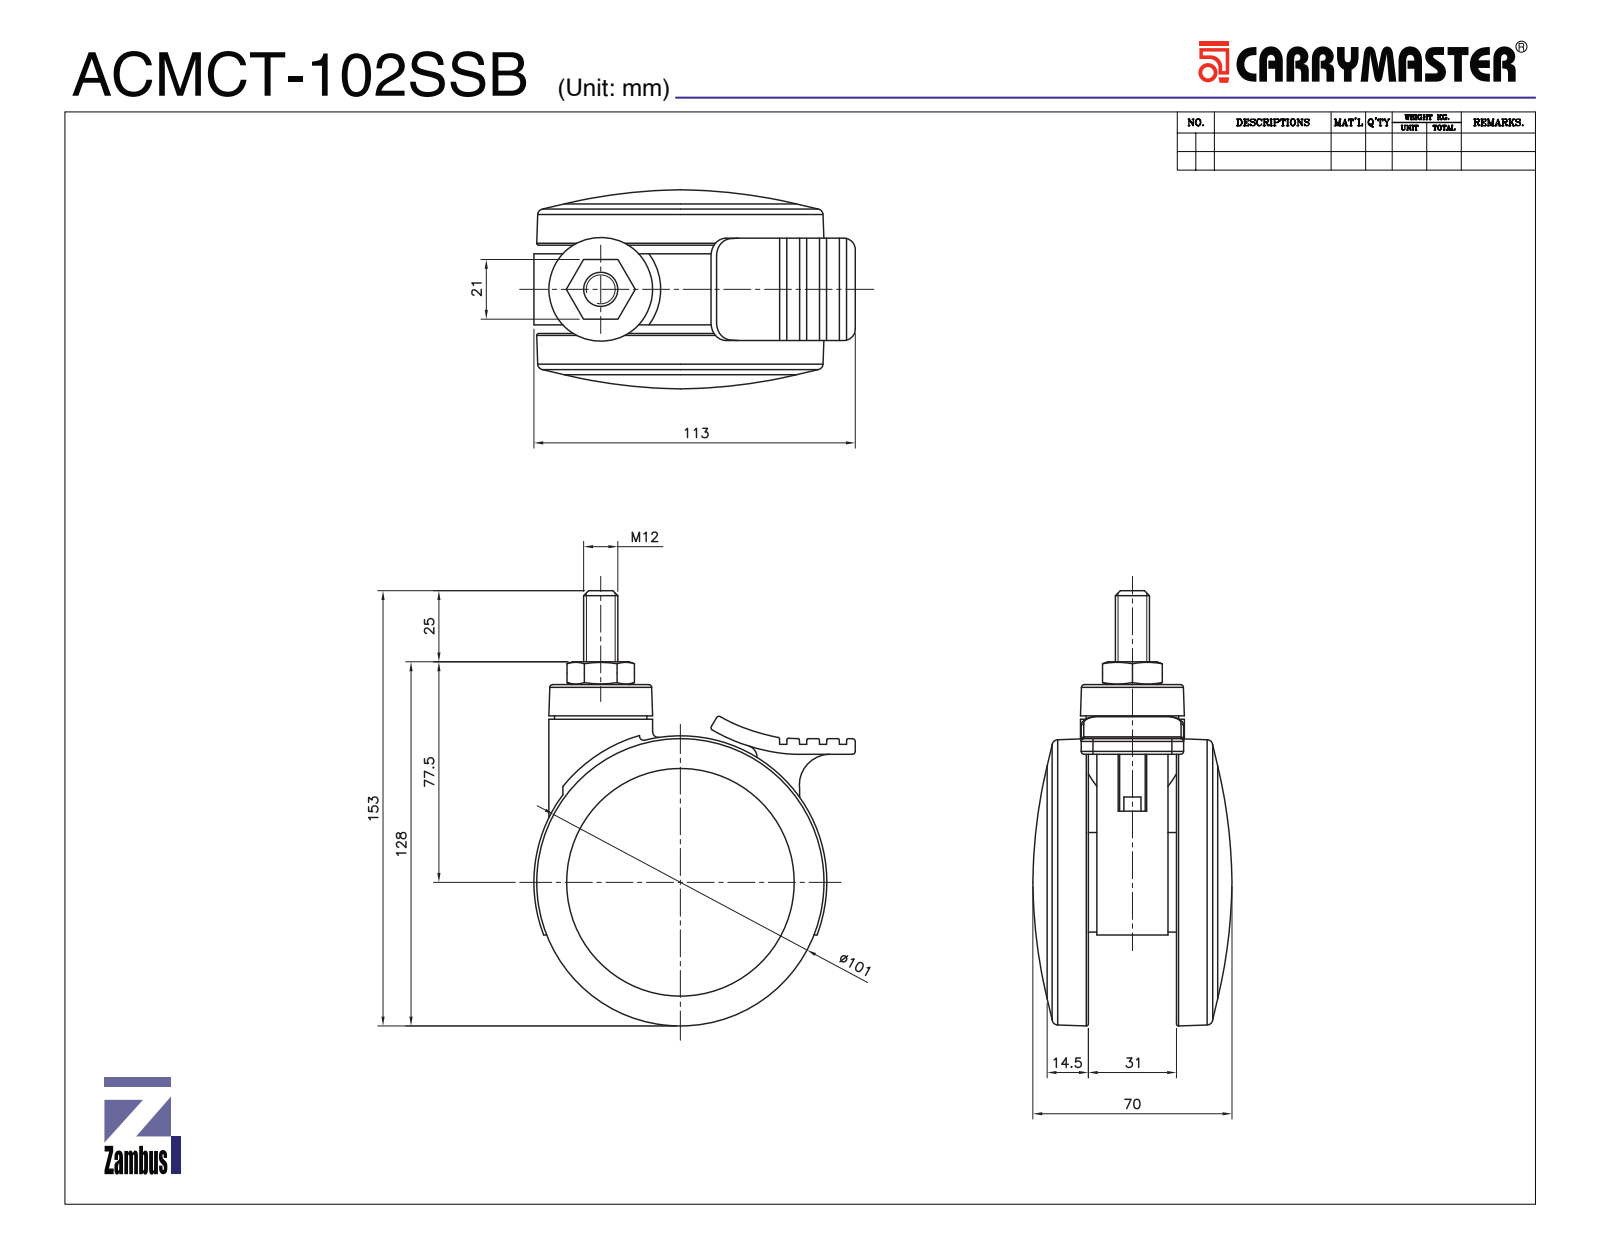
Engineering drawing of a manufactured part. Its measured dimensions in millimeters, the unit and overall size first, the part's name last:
Units: millimetres
Overall size (bounding box): 153 × 114.5 × 70
Round holes (diameter × count): ⌀25 ×1, ⌀72 ×1, ⌀80.2 ×1
Round bosses / shafts (diameter × count): ⌀80 ×1, ⌀36.7 ×1, ⌀36.5 ×1, ⌀32.5 ×1, ⌀13 ×1, ⌀12 ×1, ⌀10.25 ×1, ⌀6 ×1
Partial cylindrical surfaces — rounded edges, fillets, slot ends (radius × count): R0.5 ×72, R1 ×9, R4 ×3, R3 ×2, R5 ×2, R8.5 ×1, R11 ×1, R12 ×1
Main face-to-face distances: 3, 28, 38, 13, 10, 41, 25, 31, 51, 2.5
Volume: 372 767 mm³ · Surface area: 85 731 mm²
Bodies: 6 solids, 447 faces (128 planar, 224 cylindrical, 95 other)
Part name (STEP PRODUCT): ACMC-102 BOLT; ACMC-102 WHEEL; ACMC-102 BRAKE; ACMCT-102SSB (+2 more)
STEP written by: SolidWorks 2019 (CONFIG_CONTROL_DESIGN)
